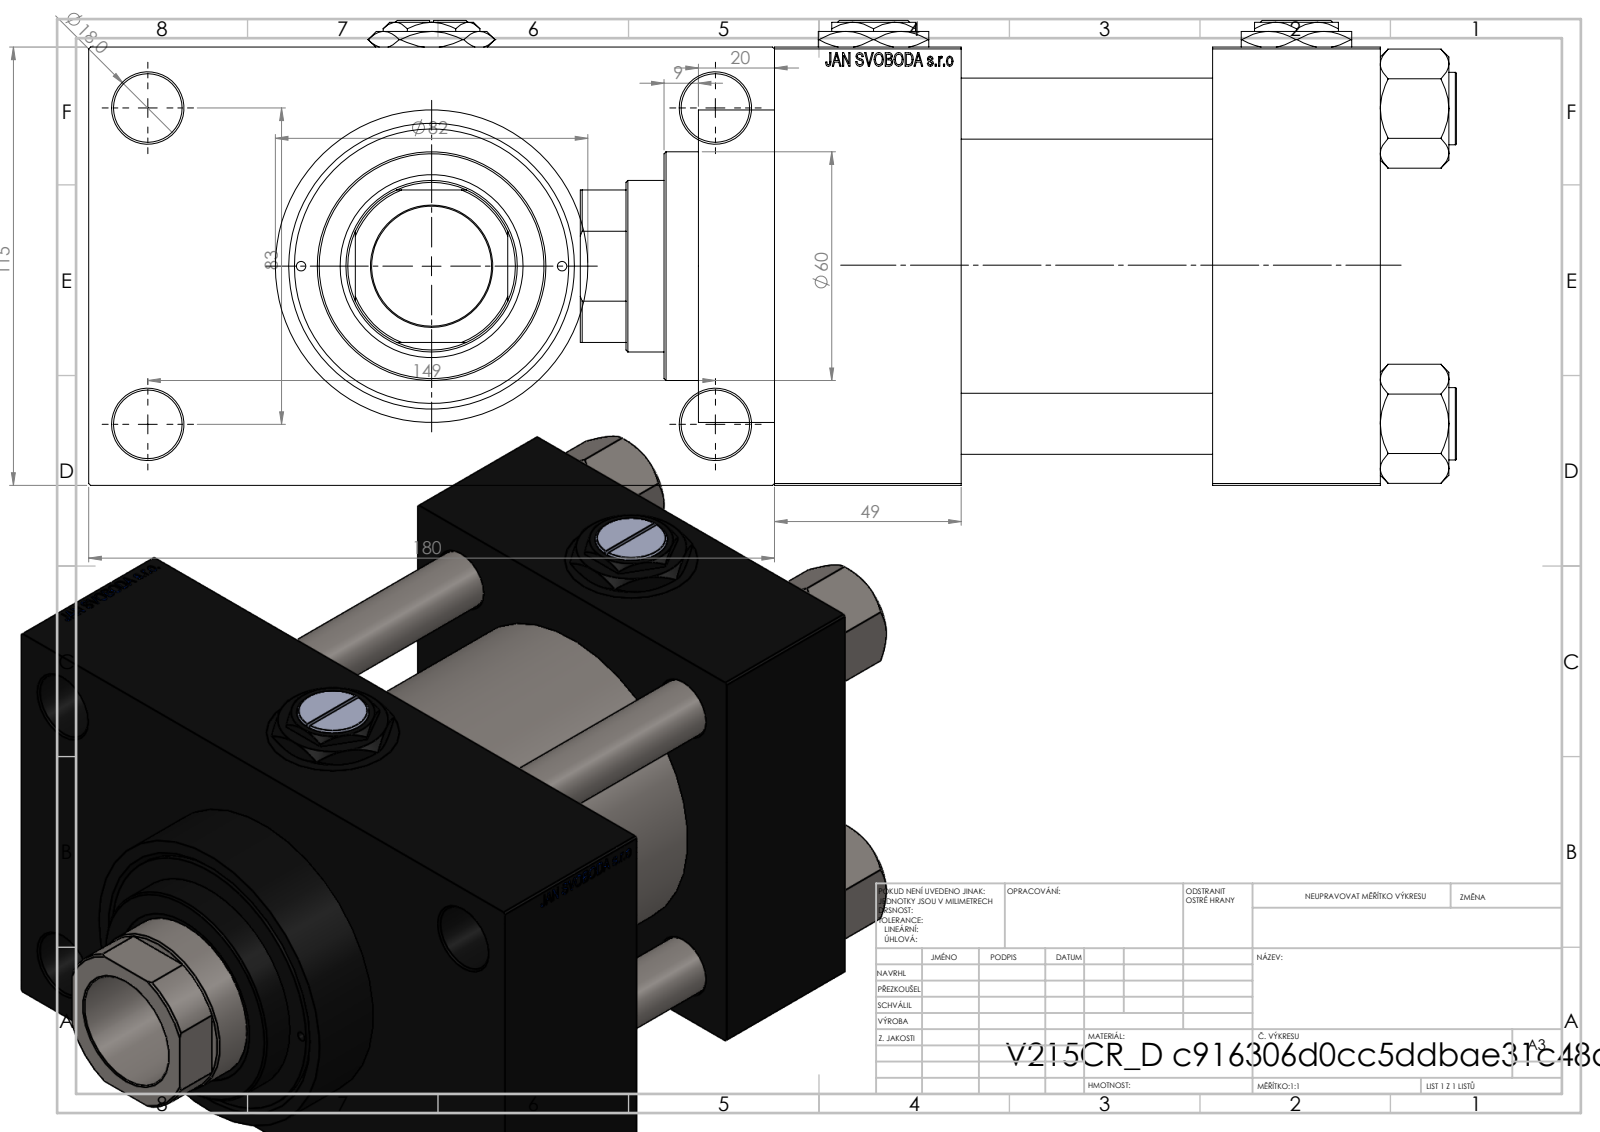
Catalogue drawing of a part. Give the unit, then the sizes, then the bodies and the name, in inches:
Units: inches
Overall size (bounding box): 9.055 × 7.087 × 4.803
Round holes (diameter × count): ⌀0.63 ×4, ⌀0.709 ×4, ⌀1.041 ×4, ⌀1.378 ×4, ⌀0.276 ×3, ⌀0.098 ×2, ⌀1.24 ×1, ⌀1.772 ×1, ⌀1.89 ×1, ⌀2.402 ×1, ⌀2.835 ×1, ⌀3.15 ×1
Round bosses / shafts (diameter × count): ⌀0.748 ×4, ⌀3.386 ×1, ⌀3.228 ×1, ⌀2.362 ×1
Partial cylindrical surfaces — rounded edges, fillets, slot ends (radius × count): R0.866 ×1
Main face-to-face distances: 4.528, 4.331, 2.598, 1.929, 1.732, 6.26, 1.28, 5.807, 0.787, 2.717
Hole centre spacings: 1.305, 1.652, 2.276, 2.302, 3.256, 3.357, 3.393, 3.513
Volume: 121.4 in³ · Surface area: 479 in²
Bodies: 13 solids, 1260 faces (595 planar, 103 cylindrical, 562 other)
Part name (STEP PRODUCT): NUT_M5_D; Zatka_pro_OIL_PORT; V215CR_D_TYCINKA; V215CR_D_Body (+2 more)
STEP written by: SolidWorks 2019 (CONFIG_CONTROL_DESIGN)
